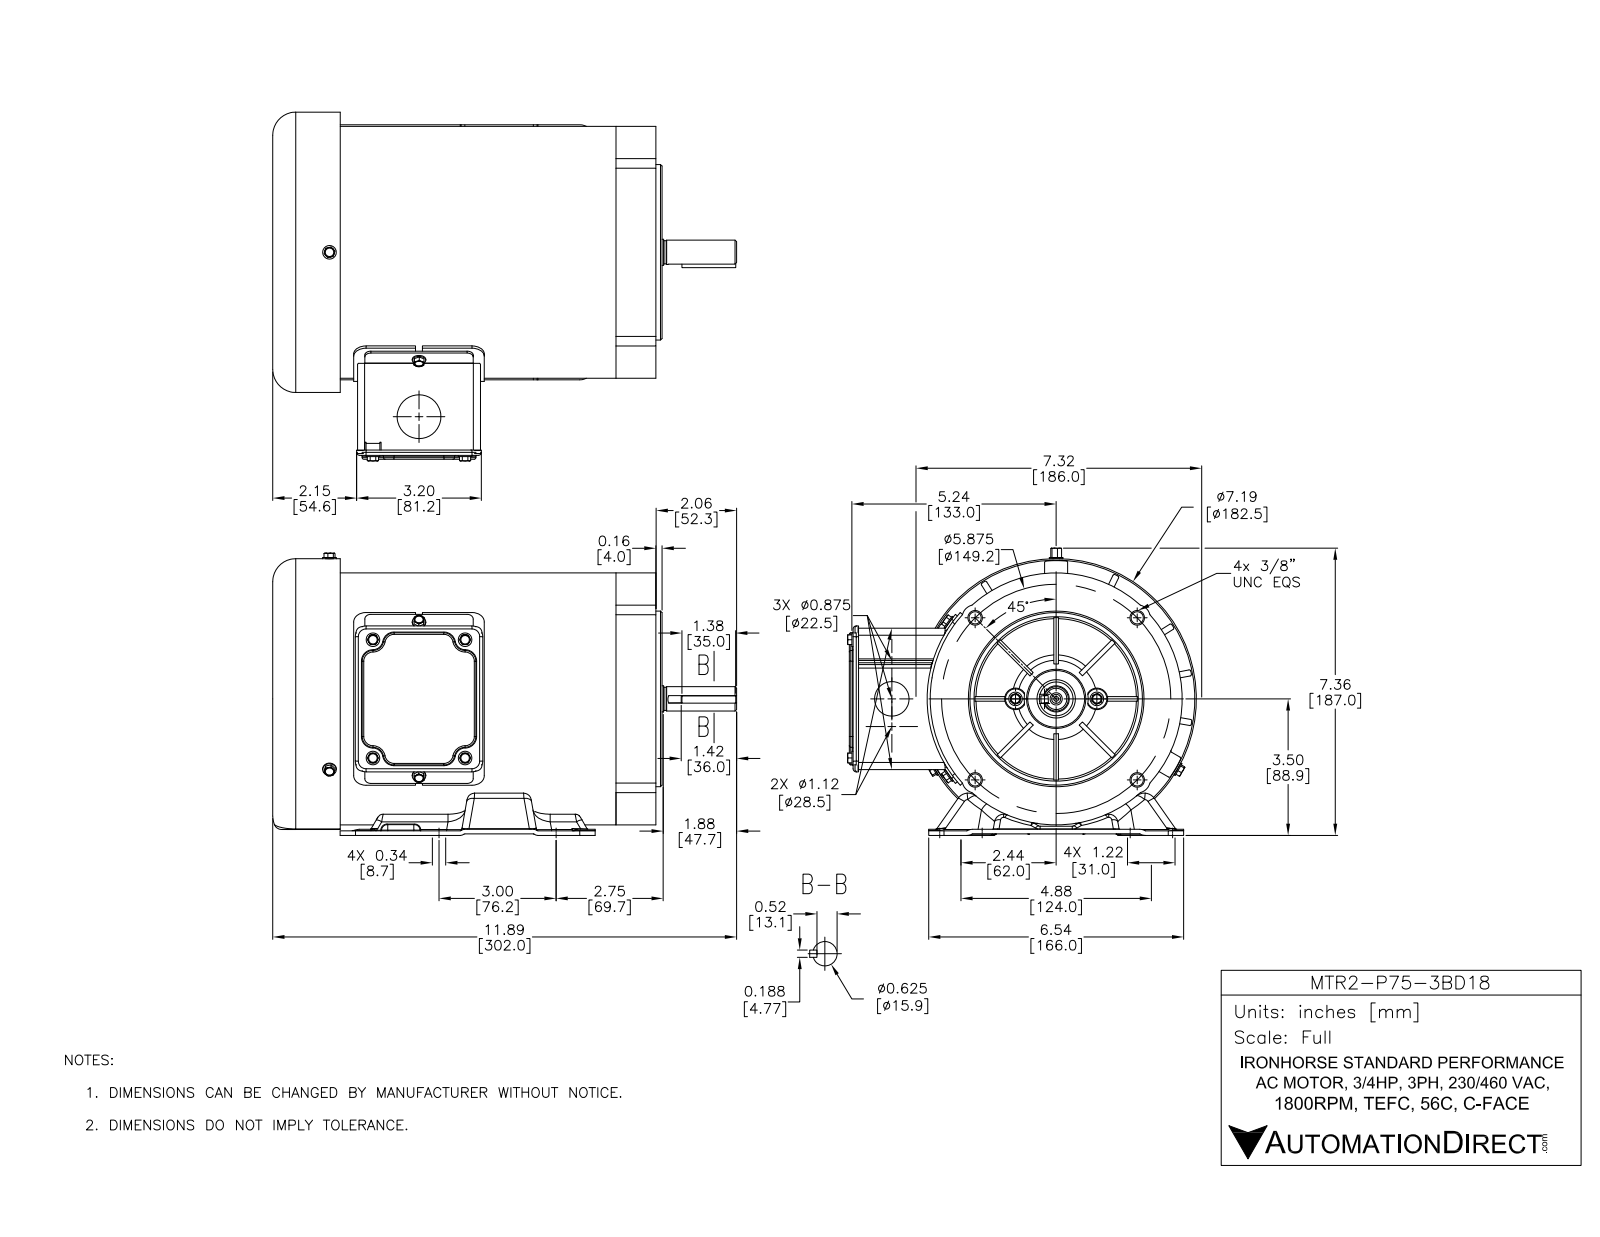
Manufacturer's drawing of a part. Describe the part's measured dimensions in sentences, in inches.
The part is named "MTR2-P75-3BD18". Its 3-D file was written by "SolidWorks 2016 (AUTOMOTIVE_DESIGN)". It is 37 solids with 2761 faces: 763 planar, 888 cylindrical and 1110 other. Overall it measures 11.634 by 8.938 by 7.234 inches. Its volume is 48.55 cubic inches and its surface area 976.3 square inches. Round holes: 12 of diameter 0.197, 11 of diameter 0.219, 8 of diameter 0.276, 6 of diameter 0.217, 6 of diameter 0.344, 5 of diameter 0.136, 4 of diameter 0.15, 4 of diameter 0.177, 4 of diameter 0.313, 2 of diameter 0.067, 2 of diameter 0.134, 2 of diameter 0.512. Round bosses or shafts: 11 of diameter 0.164, 7 of diameter 0.348, 6 of diameter 0.25, 4 of diameter 0.348, 1 of diameter 7.185, 1 of diameter 6.457, 1 of diameter 4.5, 1 of diameter 0.945. Partial cylindrical surfaces (rounded edges, fillets, slot ends): 121 of radius 0.118, 38 of radius 0.039, 32 of radius 0.02, 32 of radius 0.157, 26 of radius 0.138, 19 of radius 0.276, 12 of radius 0.172, 12 of radius 0.197. The main face-to-face distances are 0.118, 0.039, 0.063, 8.386, 1.024, 1.142, 9.528, 9.567, 3.559, 0.079. The hole center spacings are 4.221, 3.031, 0.094, 2.32, 2.409, 2.937, 2.979, 3.748.
